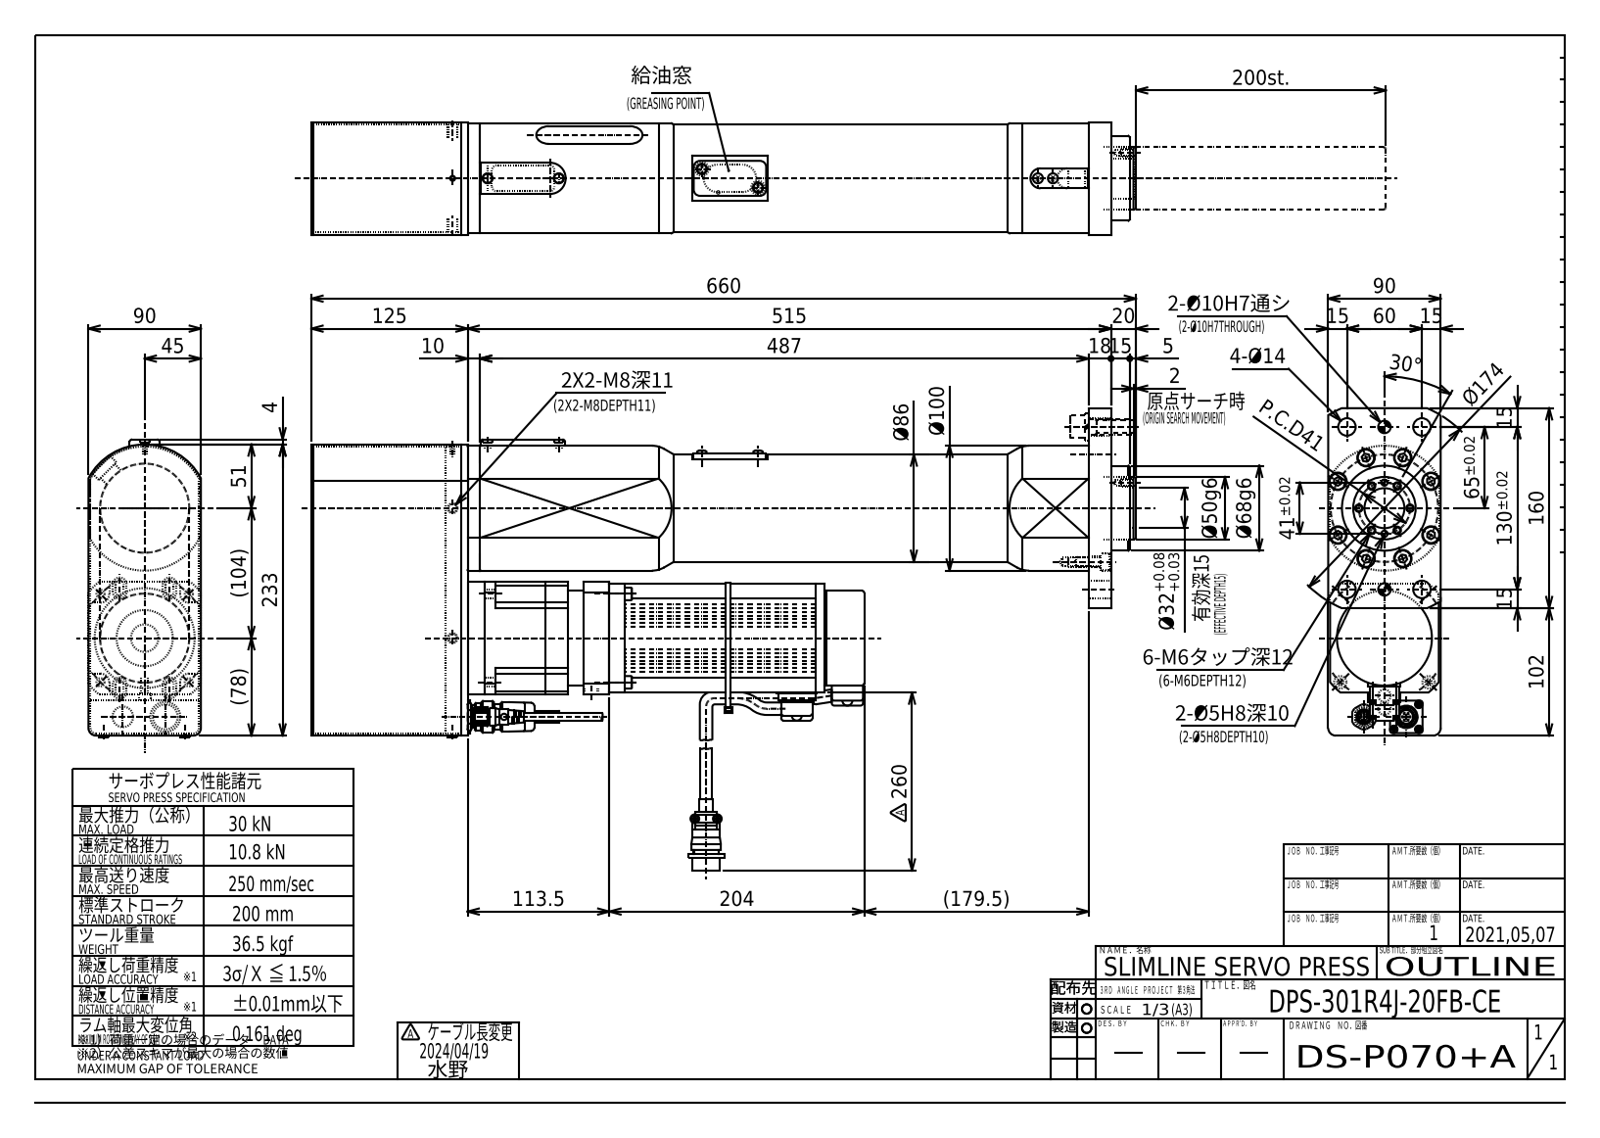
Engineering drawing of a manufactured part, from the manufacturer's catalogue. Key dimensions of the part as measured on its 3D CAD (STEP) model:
Part name (STEP PRODUCT): DPS-301R4J-20FB-CE_(DS-P070)
STEP written by: Autodesk Inventor 2021 (AUTOMOTIVE_DESIGN)
Units: millimetres
Bodies: 1 solid, 1806 faces (1019 planar, 513 cylindrical, 274 other)
Overall size (bounding box): 660 × 263.5 × 90
Volume: 8 131 000 mm³ · Surface area: 515 333 mm²
Round holes (diameter × count): ⌀6.65 ×12, ⌀14 ×12, ⌀4.92 ×10, ⌀5.5 ×10, ⌀9 ×8, ⌀4.2 ×6, ⌀9.5 ×6, ⌀8 ×4, ⌀5 ×3, ⌀4.5 ×2, ⌀10 ×2, ⌀11 ×2
Round bosses / shafts (diameter × count): ⌀8 ×16, ⌀13 ×8, ⌀7 ×6, ⌀3 ×6, ⌀10 ×4, ⌀8.5 ×4, ⌀7.5 ×4, ⌀4 ×4
Partial cylindrical surfaces — rounded edges, fillets, slot ends (radius × count): R0.6 ×48, R1 ×26, R0.3 ×20, R2 ×16, R3 ×10, R4.5 ×10, R5 ×10, R1.5 ×8
Main face-to-face distances: 1.5, 90, 1, 3, 88.5, 89, 4.5, 16.5, 7.5, 6
Hole centre spacings: 20.5, 43, 27.25, 61.61, 80.82, 10.61, 23.09, 24.75
